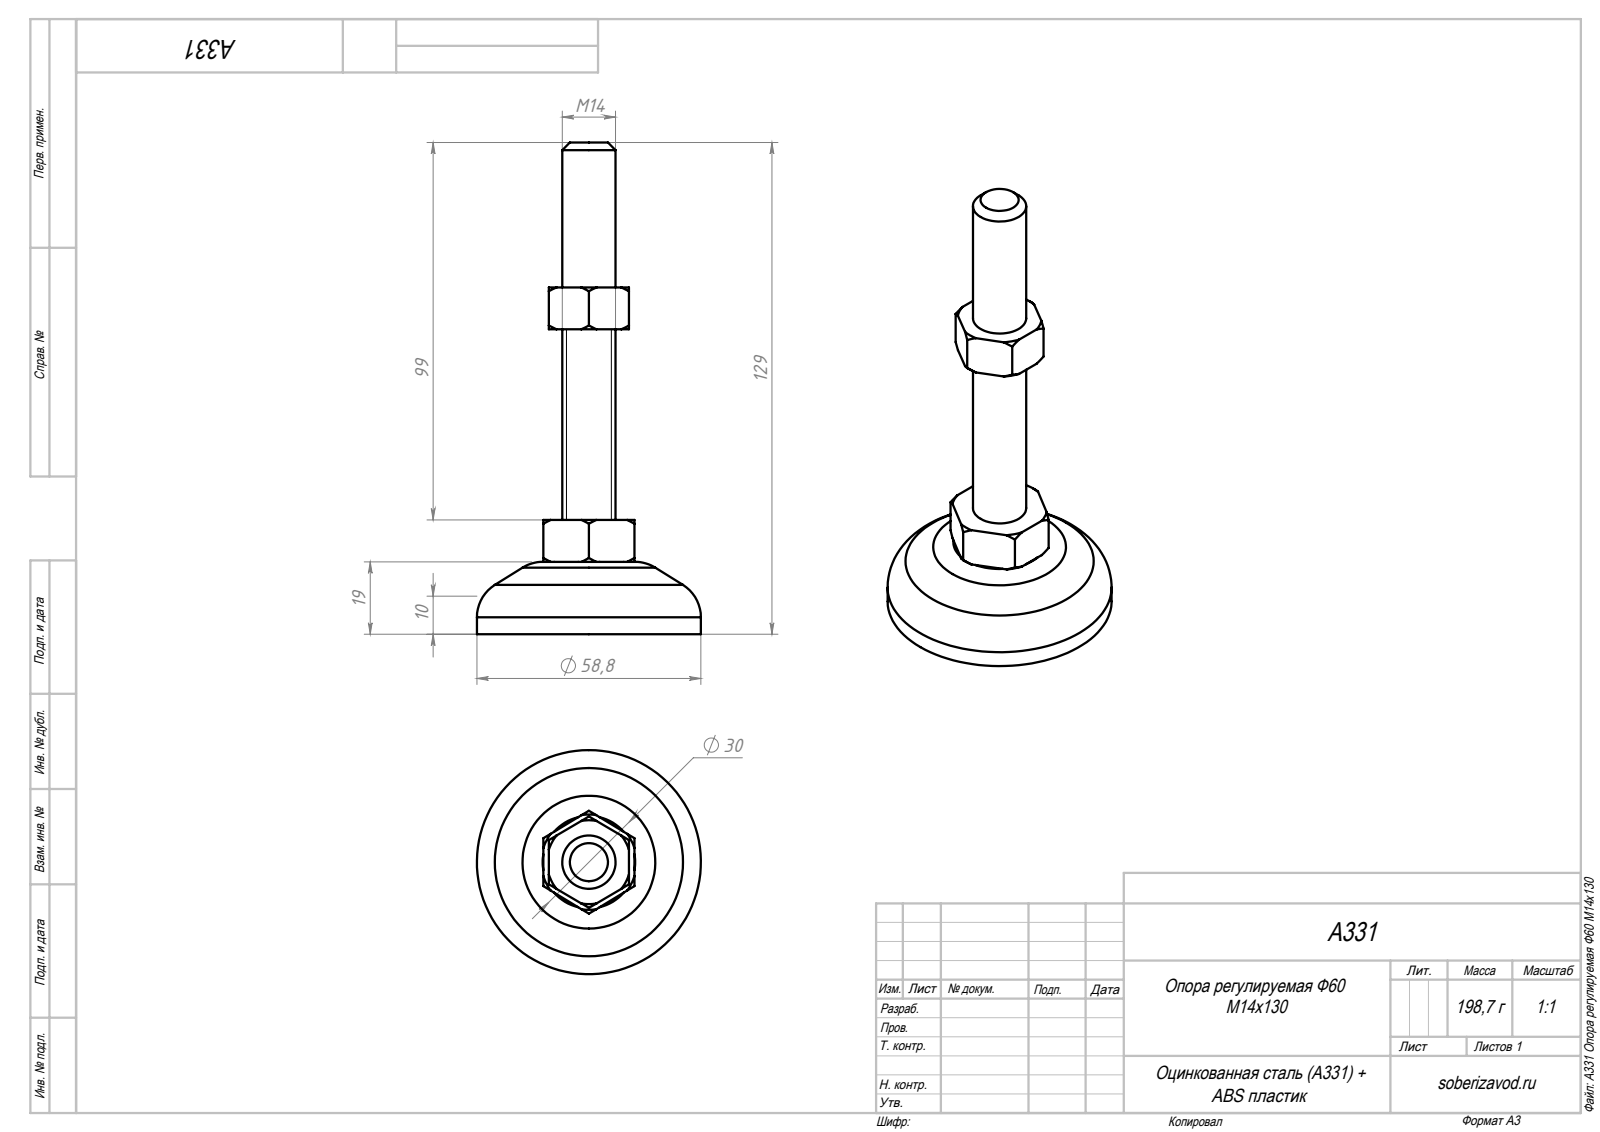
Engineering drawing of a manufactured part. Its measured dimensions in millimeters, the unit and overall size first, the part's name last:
Units: millimetres
Overall size (bounding box): 129 × 58.8 × 58.8
Round bosses / shafts (diameter × count): ⌀58.8 ×1, ⌀14 ×1
Main face-to-face distances: 30, 1.45, 22.45, 61, 11, 91, 80, 50, 23.12, 23.1
Volume: 63 414 mm³ · Surface area: 13 349 mm²
Bodies: 1 solid, 65 faces (23 planar, 6 cylindrical, 36 other)
Part name (STEP PRODUCT): A331 Опора регулируемая Ф60 М14х130
STEP written by: SolidWorks 2018 (AUTOMOTIVE_DESIGN)
